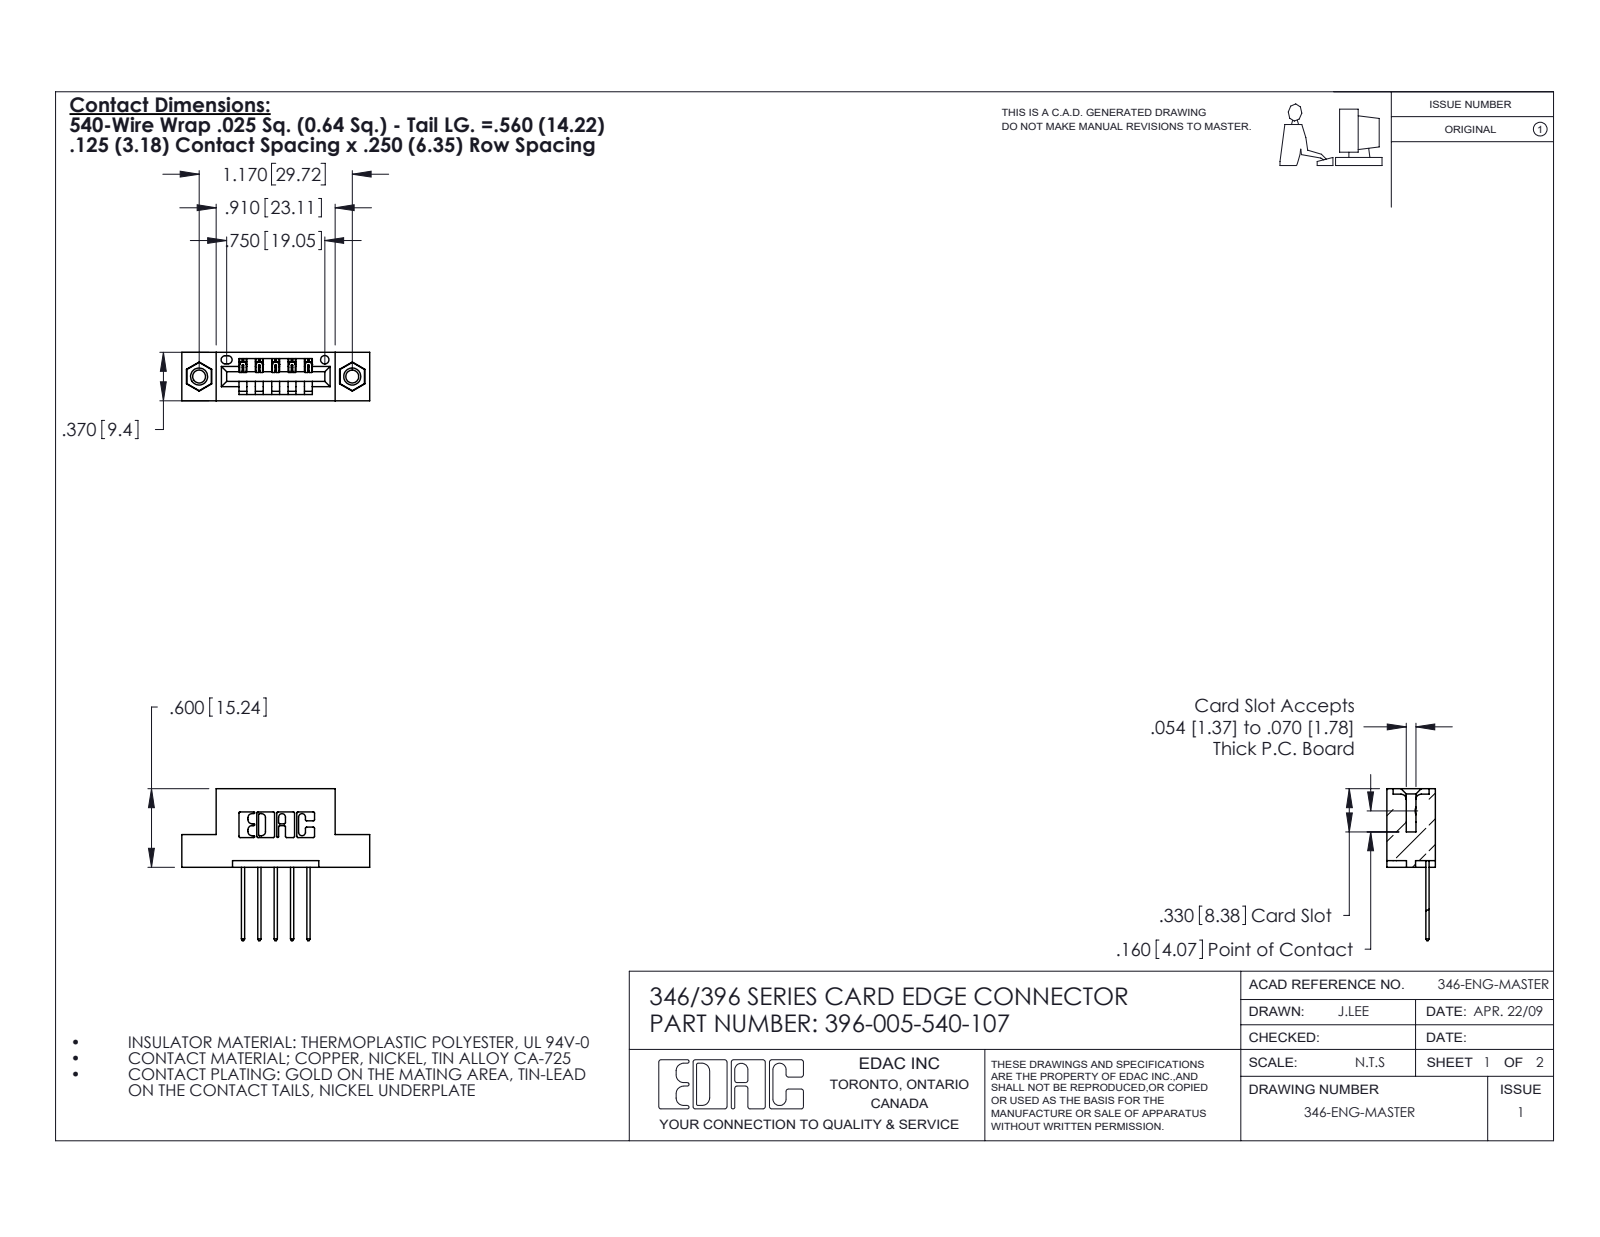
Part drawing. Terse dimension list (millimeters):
name: 346 Part_Flush Mounting Lugs - 0.156 Dia-TI; 345-292-001_345-293-140; 396-005-540-107; 345-250-001_345-250-005-103
written by: SolidWorks 2020 (CONFIG_CONTROL_DESIGN)
unit: mm
bodies: 8 solids, 472 faces (308 planar, 148 cylindrical, 16 other)
size: 36.4 × 29.5 × 9.4
volume: 3 230 mm³; area: 3 719 mm²
holes: 2× ⌀2.5, 2× ⌀3.2, 2× ⌀4, 1× ⌀1.6
bosses: 2× ⌀3.9
rounds: 22× R0.3, 10× R0.2, 10× R0.3, 6× R0.2, 6× R0.8, 3× R0.7, 2× R0.8, 2× R1
face distances: 6.4, 9.4, 1.2, 8.2, 1.8, 7.6, 0.6, 14, 3.8, 5.6
hole spacings: 6.2, 24.6, 29.7
